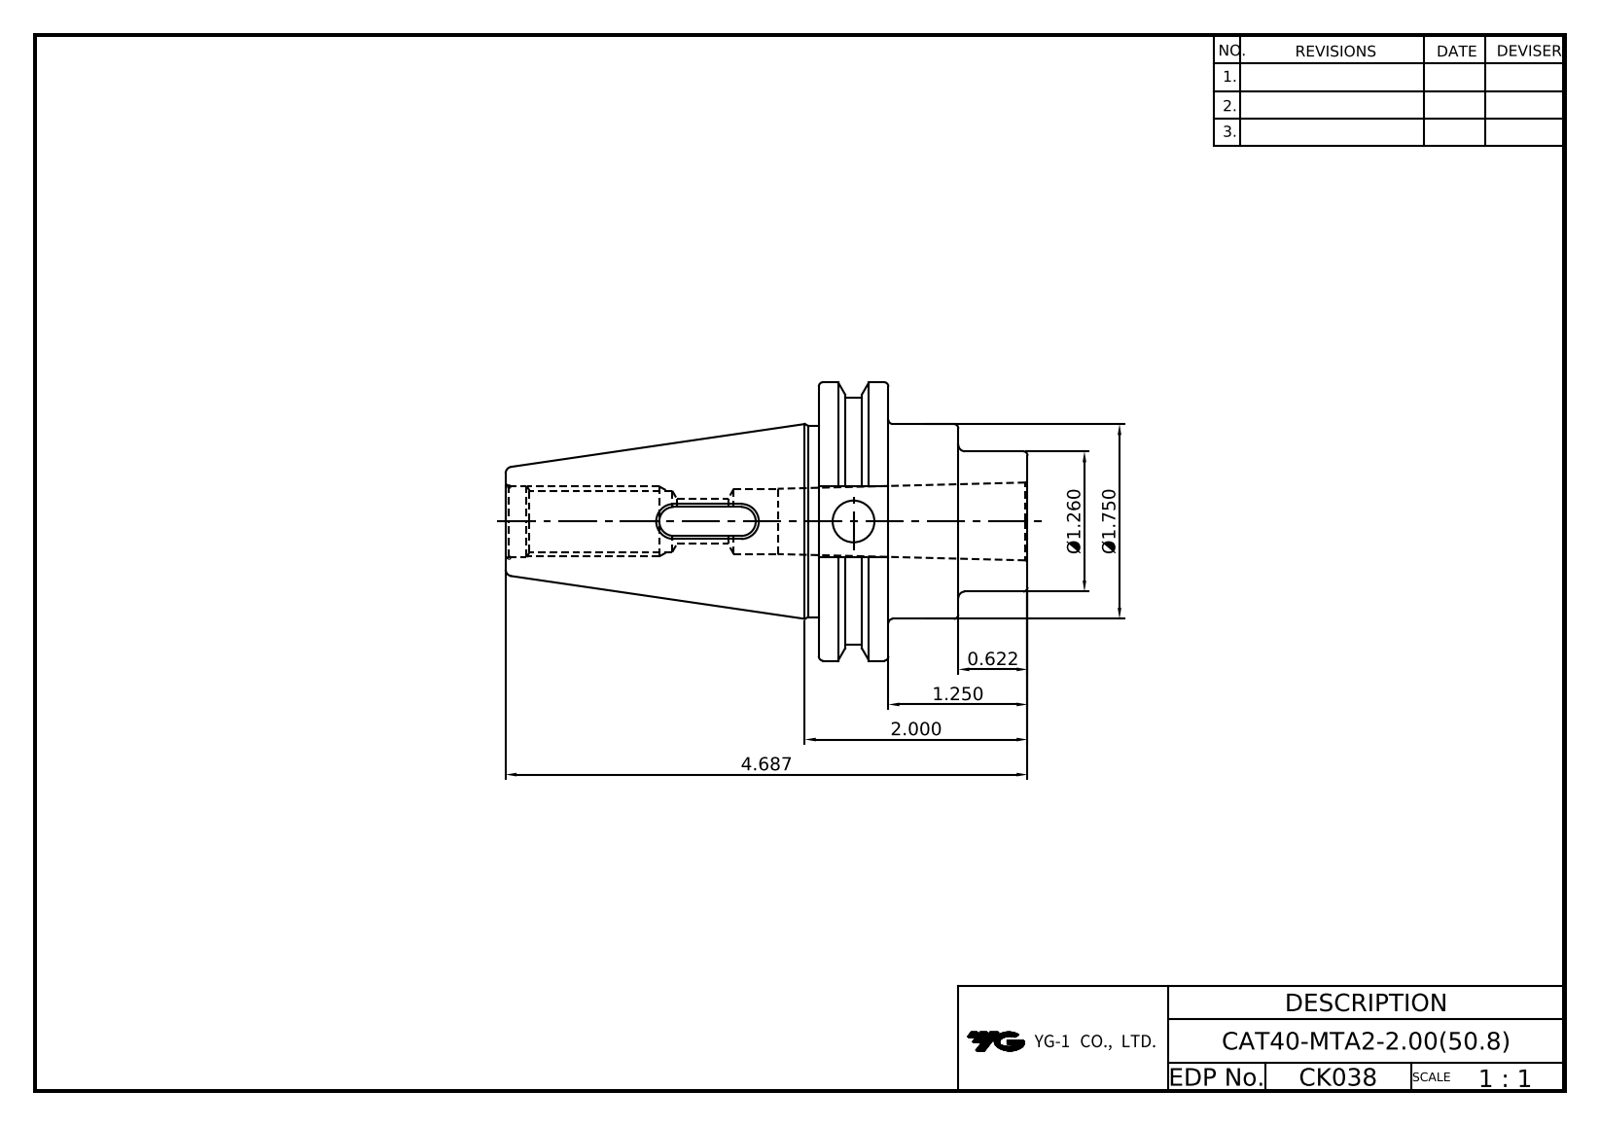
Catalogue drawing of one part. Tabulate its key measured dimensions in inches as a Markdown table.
| quantity | value |
| --- | --- |
| part name | LO-CAT40-MTA2-50.8 |
| STEP written by | Autodesk Inventor 2025 (AUTOMOTIVE_DESIGN) |
| units | inches |
| bodies | 1 solid, 91 faces (34 planar, 19 cylindrical, 38 other) |
| overall size | 4.687 × 2.5 × 2.405 |
| volume | 7.749 in³ |
| surface area | 40.62 in² |
| round holes (diameter × count) | 0.375 × 1, 0.527 × 1, 0.587 × 1, 0.642 × 1 |
| round bosses / shafts (diameter × count) | 2.5 × 1, 2.217 × 1, 1.75 × 1, 1.717 × 1, 1.26 × 1 |
| partial cylindrical surfaces (radius × count) | 0.124 × 2, 0.203 × 1 |
| main face-to-face distances | 0.625, 1.253, 0.628, 0.248, 1.875, 1.25, 0.622, 0.198, 0.446, 1.874 |
